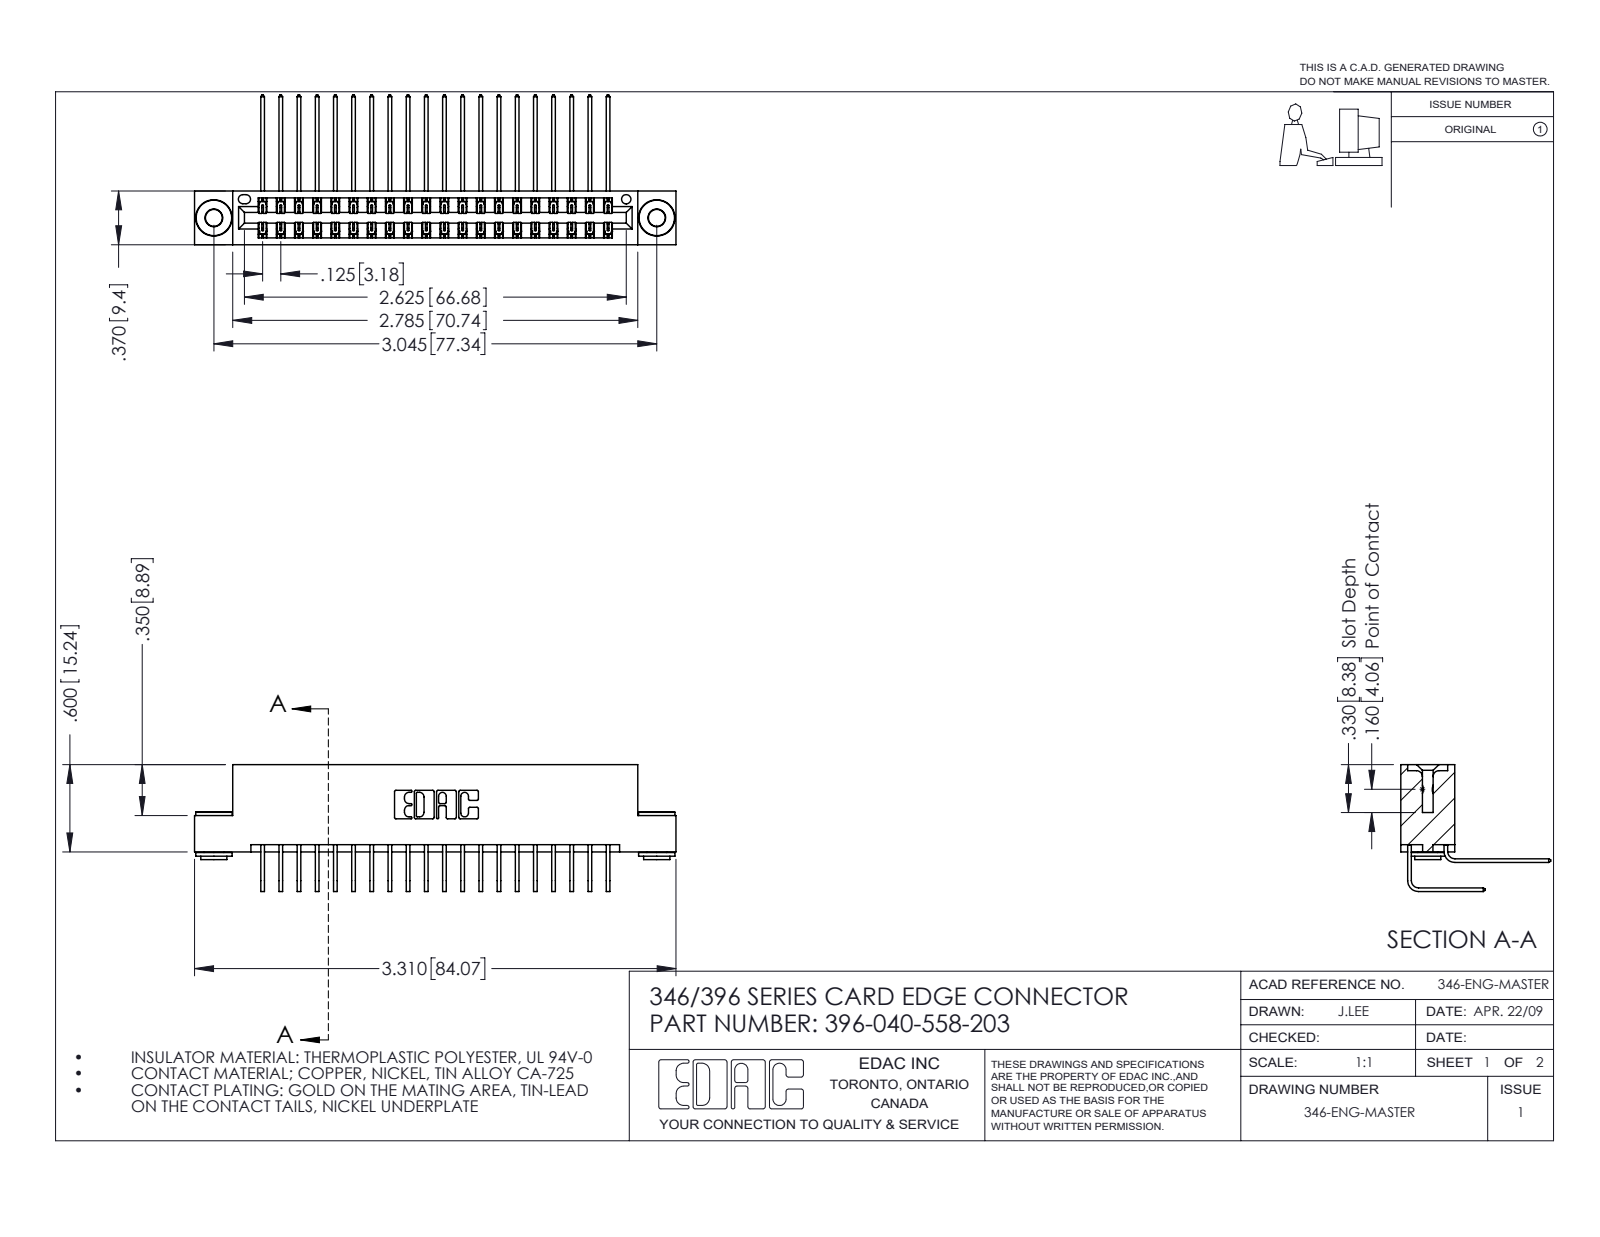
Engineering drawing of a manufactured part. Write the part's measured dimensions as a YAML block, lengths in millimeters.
part_name: "345-292-001_558 559 Tail - 1; 345-292-001_558 Tail - 2; 345-250-002_345-250-002-102; 396-040-558-203 (+1 more)"
step_written_by: "SolidWorks 2016 (CONFIG_CONTROL_DESIGN)"
units: millimeters
bodies: {solids: 43, faces: 2320, planar: 1566, cylindrical: 746, other: 8}
overall_size: [84.1, 26.2, 22.2]
volume: 8280
surface_area: 12350
round_holes:
  - {diameter: 2.9, count: 2}
  - {diameter: 4, count: 2}
  - {diameter: 1.6, count: 1}
round_bosses_or_shafts:
  - {diameter: 6.4, count: 2}
  - {diameter: 4.6, count: 2}
  - {diameter: 3.5, count: 2}
partial_cylinders:
  - {radius: 0.2, count: 60}
  - {radius: 0.3, count: 22}
  - {radius: 0.2, count: 6}
  - {radius: 0.8, count: 6}
  - {radius: 0.7, count: 3}
  - {radius: 0.4, count: 2}
  - {radius: 0.6, count: 2}
  - {radius: 0.6, count: 2}
face_to_face_distances: [8.2, 1.2, 6.4, 0.6, 9.4, 7.6, 1.8, 7, 3.8, 5.6]
hole_center_spacings: [6.2, 72.1, 77.3]
